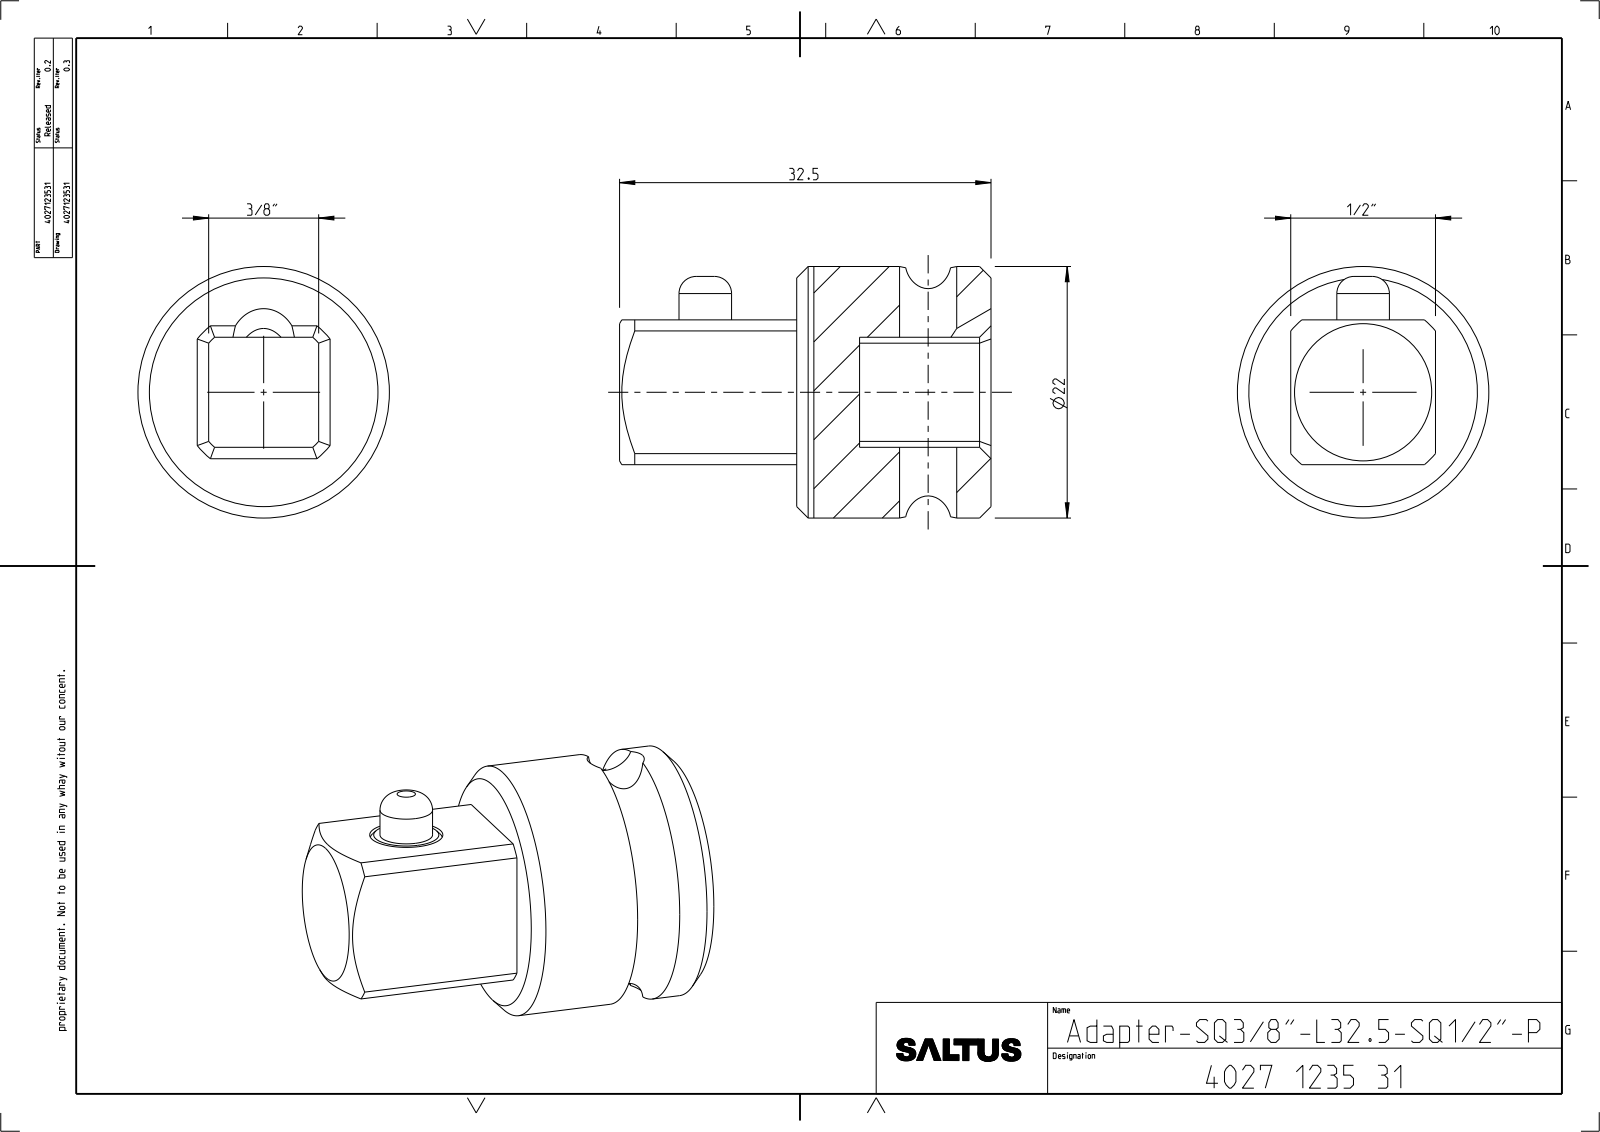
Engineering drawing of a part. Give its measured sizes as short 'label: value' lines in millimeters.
name: 4027123531
written by: CREO PARAMETRIC BY PTC INC, 2022414 (CONFIG_CONTROL_DESIGN)
unit: mm
bodies: 2 solids, 67 faces (22 planar, 23 cylindrical, 22 other)
size: 32.5 × 22 × 22
volume: 6 947 mm³; area: 3 622 mm²
holes: 1× ⌀5, 1× ⌀6.4
bosses: 1× ⌀22, 1× ⌀6.3, 1× ⌀4.6
rounds: 1× R3, 1× R6.45, 1× R8.3
face distances: 1.52, 11.14, 12.66, 17, 9.62, 32.5, 15.5, 11.5, 5.5, 21
hole spacings: 19.5
